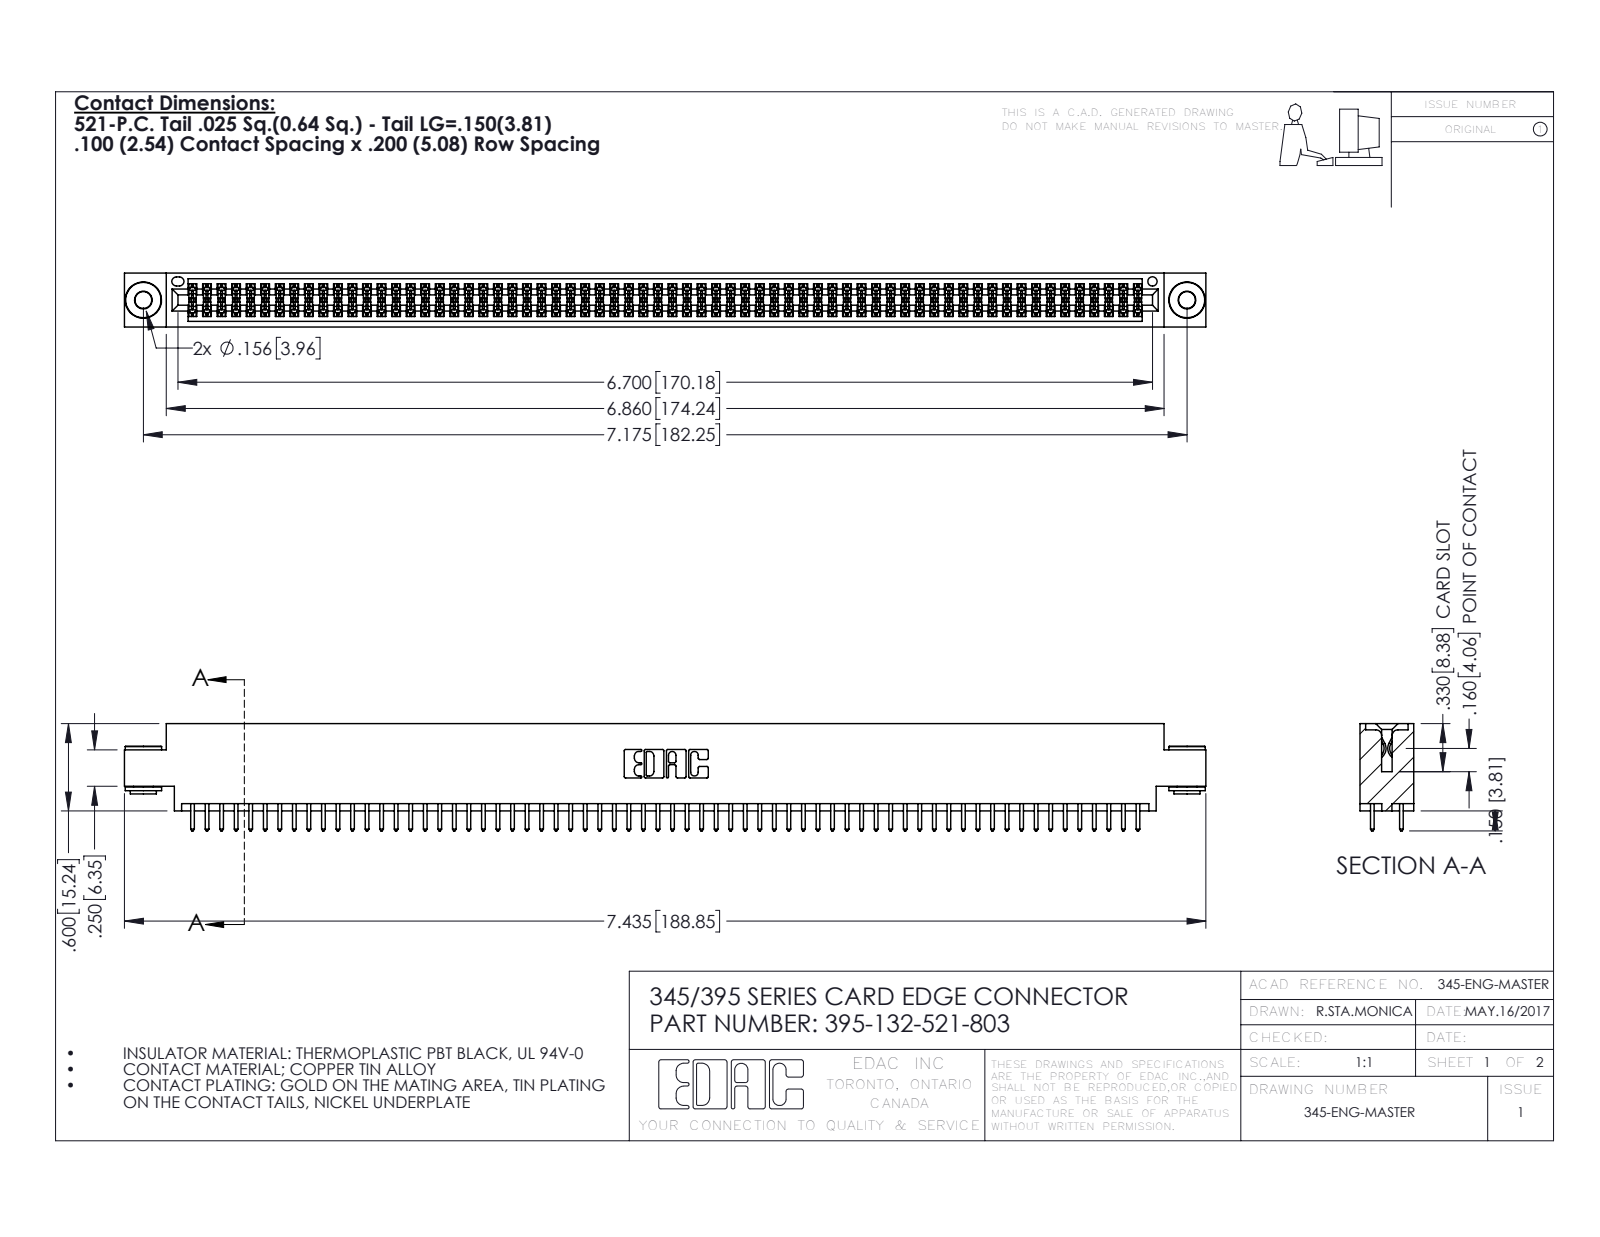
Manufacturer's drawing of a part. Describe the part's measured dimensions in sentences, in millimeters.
The part is named "345-292-001_345-293-121; 345 Part_0.170 Offset - 0.156 Dia-TH; 345-250-002_345-250-002-102; 395-132-521-803". Its 3-D file was written by "SolidWorks 2016 (CONFIG_CONTROL_DESIGN)". It is 135 solids with 6768 faces: 4450 planar, 2310 cylindrical and 8 other. Overall it measures 188.8 by 18.7 by 9.4 millimeters. Its volume is 18 420 cubic millimeters and its surface area 27 690 square millimeters. Round holes: 2 of diameter 2.9, 2 of diameter 4, 1 of diameter 1.6. Round bosses or shafts: 2 of diameter 6.4, 2 of diameter 4.6, 2 of diameter 3.5. Partial cylindrical surfaces (rounded edges, fillets, slot ends): 198 of radius 0.2, 132 of radius 0.3, 22 of radius 0.3, 6 of radius 0.2, 6 of radius 0.8, 3 of radius 0.7, 2 of radius 0.4, 2 of radius 0.5. The main face-to-face distances are 1.8, 7.6, 5.1, 9.4, 2.5, 6.9, 0.6, 5.7, 4.4, 3.8. The hole center spacings are 6.9, 176.3, 182.2.
